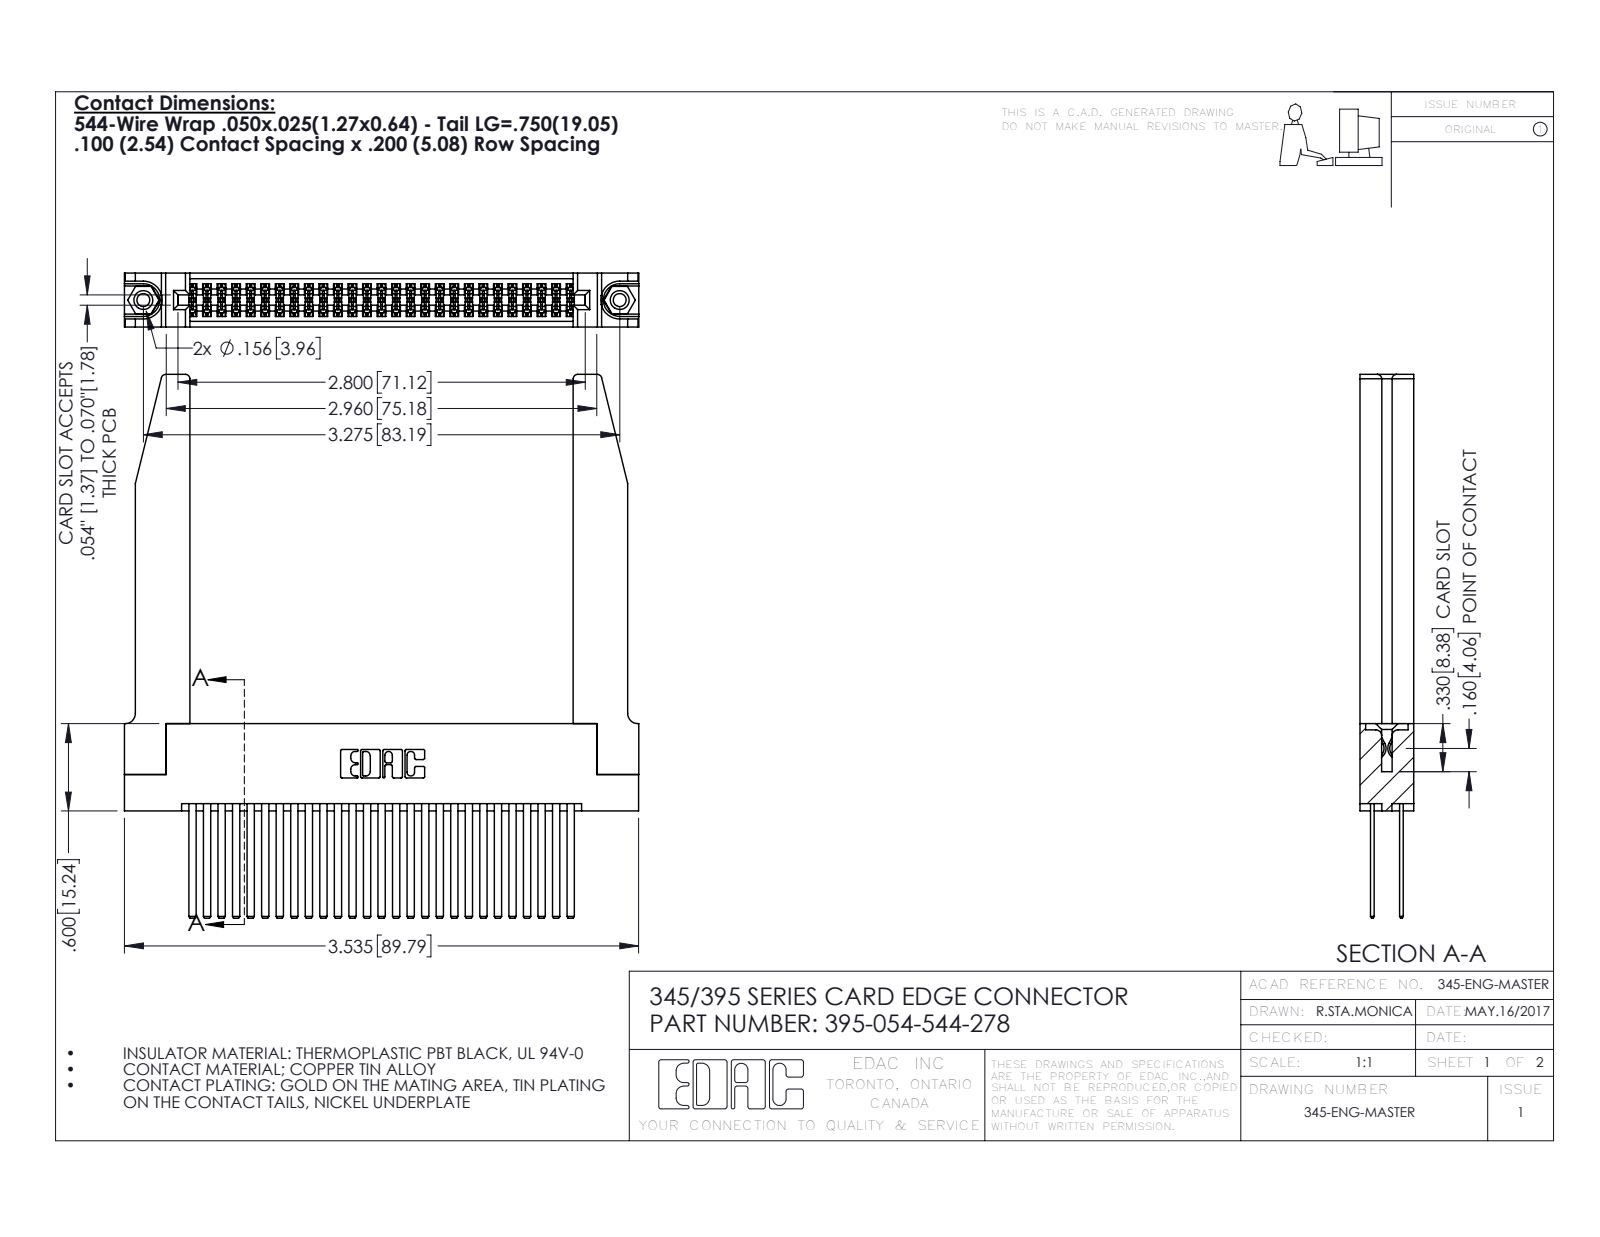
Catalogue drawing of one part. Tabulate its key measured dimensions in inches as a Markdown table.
| quantity | value |
| --- | --- |
| part name | 395-054-544-278; 345 Part_Flush Mounting Lugs - 0.156 Dia-TH; 345-250-001_345-250-001-102; 345-292-001_345-293-144 (+1 more) |
| STEP written by | SolidWorks 2016 (CONFIG_CONTROL_DESIGN) |
| units | inches |
| bodies | 59 solids, 2736 faces (1788 planar, 896 cylindrical, 52 other) |
| overall size | 3.737 × 3.536 × 0.37 |
| volume | 1.044 in³ |
| surface area | 34.99 in² |
| round holes (diameter × count) | 0.089 × 2, 0.125 × 2, 0.156 × 2, 0.064 × 1 |
| round bosses / shafts (diameter × count) | 0.155 × 2 |
| partial cylindrical surfaces (radius × count) | 0.006 × 81, 0.01 × 22, 0.03 × 8, 0.007 × 6, 0.031 × 6, 0.026 × 3, 0.014 × 2, 0.019 × 2 |
| main face-to-face distances | 0.072, 0.298, 0.2, 0.37, 0.098, 0.272, 0.025, 0.225, 0.175, 0.148 |
| hole center spacings | 0.27, 3.04, 3.275 |
